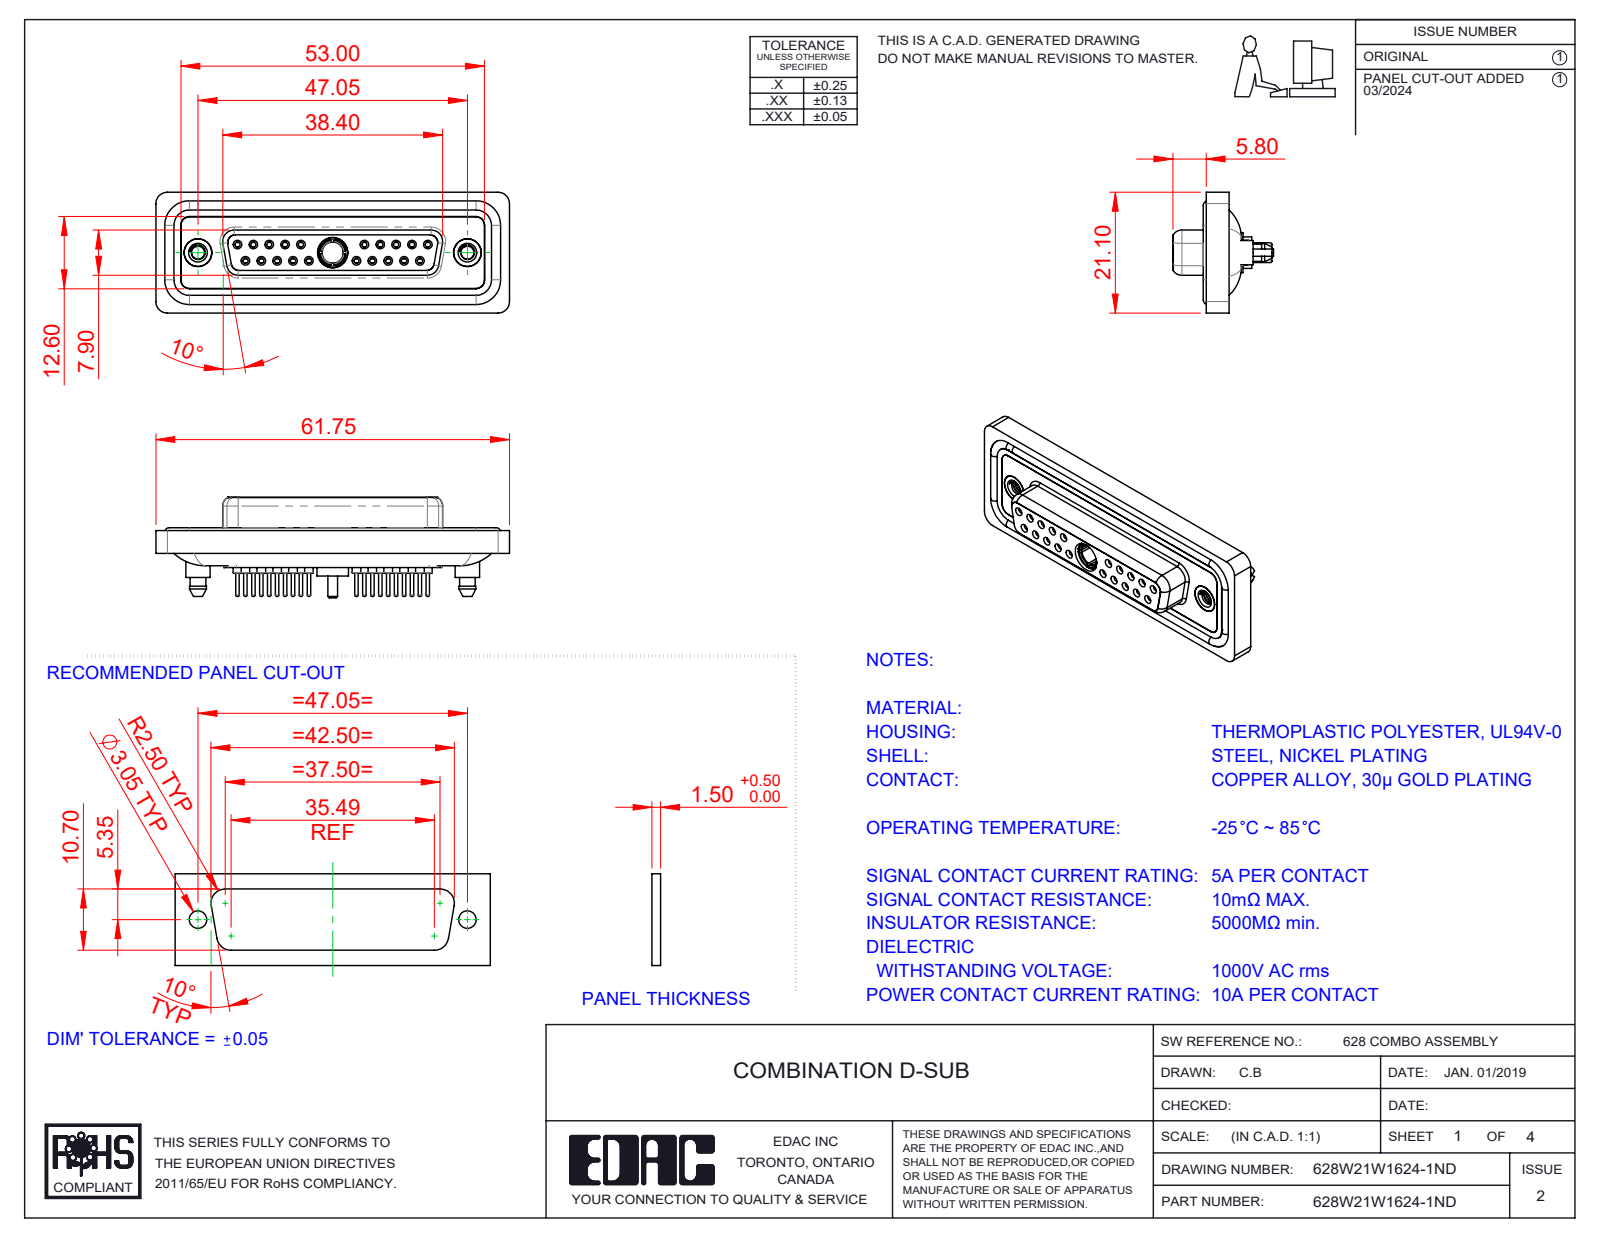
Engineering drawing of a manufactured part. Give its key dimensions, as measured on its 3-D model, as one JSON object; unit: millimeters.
{"part_name": "628Combo Contact Row 1_24; 628Combo Shell Rear_25 Contacts; 628Combo Threaded Boardlock_D; 628W21W1624-1ND (+5 more)", "step_written_by": "SolidWorks 2023 (CONFIG_CONTROL_DESIGN)", "units": "millimeters", "bodies": {"solids": 29, "faces": 1626, "planar": 450, "cylindrical": 639, "other": 537}, "overall_size": [61.75, 21.1, 17.55], "volume_mm3": 8495, "surface_area_mm2": 14329, "round_holes": [[0.9, 20], [1.1, 20], [1.5, 20], [2, 20], [1.6, 10], [1.7, 10], [4.85, 3], [2.26, 2], [4, 2], [4.05, 2], [5, 2], [3.7, 1]], "round_bosses_or_shafts": [[2.2, 20], [0.6, 20], [1.6, 14], [5.4, 2], [4.95, 2], [4.8, 2], [4.25, 2], [5.5, 1]], "partial_cylinders_radius": [[1.5, 24], [2, 18], [1.6, 10], [1.35, 8], [0.25, 4], [0.5, 4], [0.6, 4], [0.65, 4]], "face_to_face_distances": [0.4, 1.8, 7.45, 6.6, 5.65, 1.6, 0.5, 7.05, 2.9, 1.1], "hole_center_spacings": [3.16, 2.77, 5.54, 5.03, 8.31, 7.48, 16.62, 19.39]}
